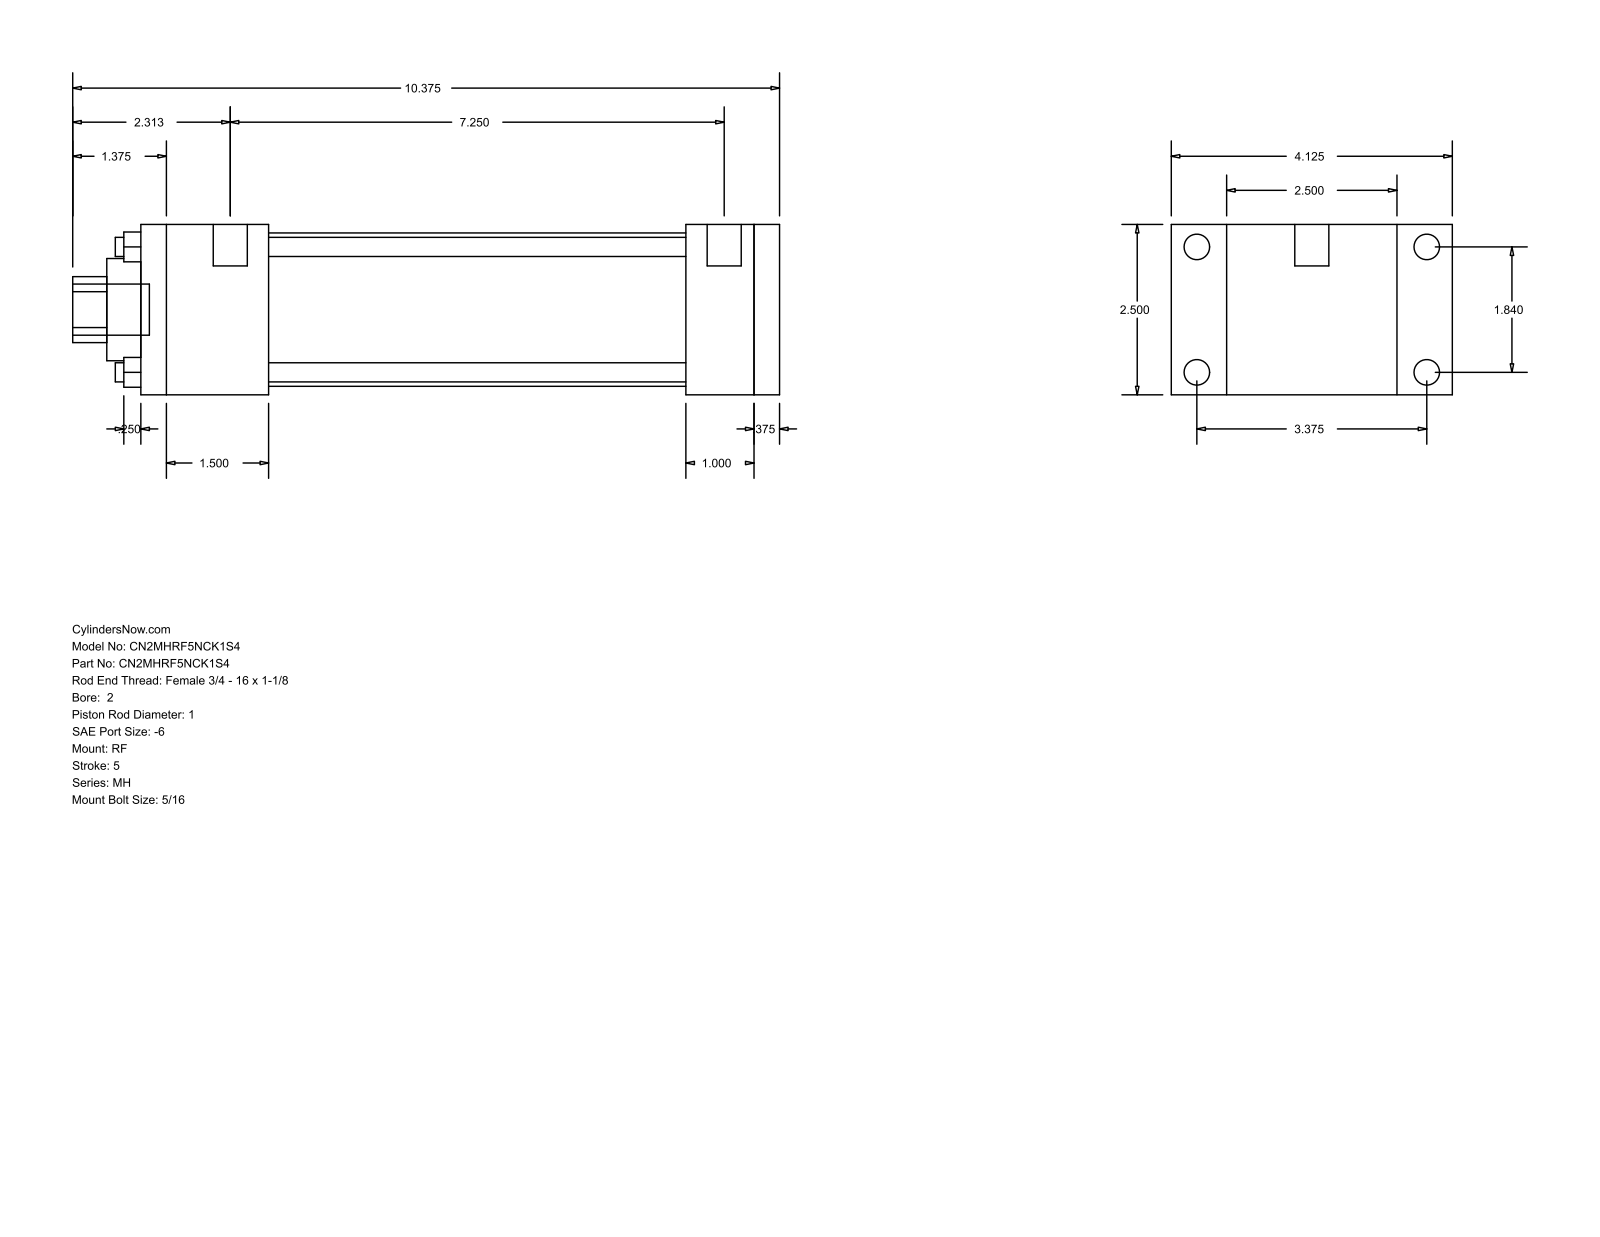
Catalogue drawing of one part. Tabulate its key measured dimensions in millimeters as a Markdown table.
| quantity | value |
| --- | --- |
| part name | MH_RF__0200_1 |
| STEP written by | GSSL Pune (CONFIG_CONTROL_DESIGN) |
| units | millimeters |
| bodies | 0 solids, 92 faces (64 planar, 28 cylindrical, 0 other) |
| overall size | 263.52 × 104.78 × 63.5 |
| round holes (diameter × count) | 7.14 × 4, 25.4 × 1, 38.1 × 1, 57.15 × 1 |
| round bosses / shafts (diameter × count) | 9.53 × 4, 5.56 × 4, 12.7 × 2, 19.05 × 1 |
| partial cylindrical surfaces (radius × count) | 12.29 × 1 |
| main face-to-face distances | 63.5, 9.52, 238.12, 228.6, 20.64, 25.4, 47.63, 203.2, 155.57, 180.97 |
| hole center spacings | 33.05, 46.74, 66.1 |
